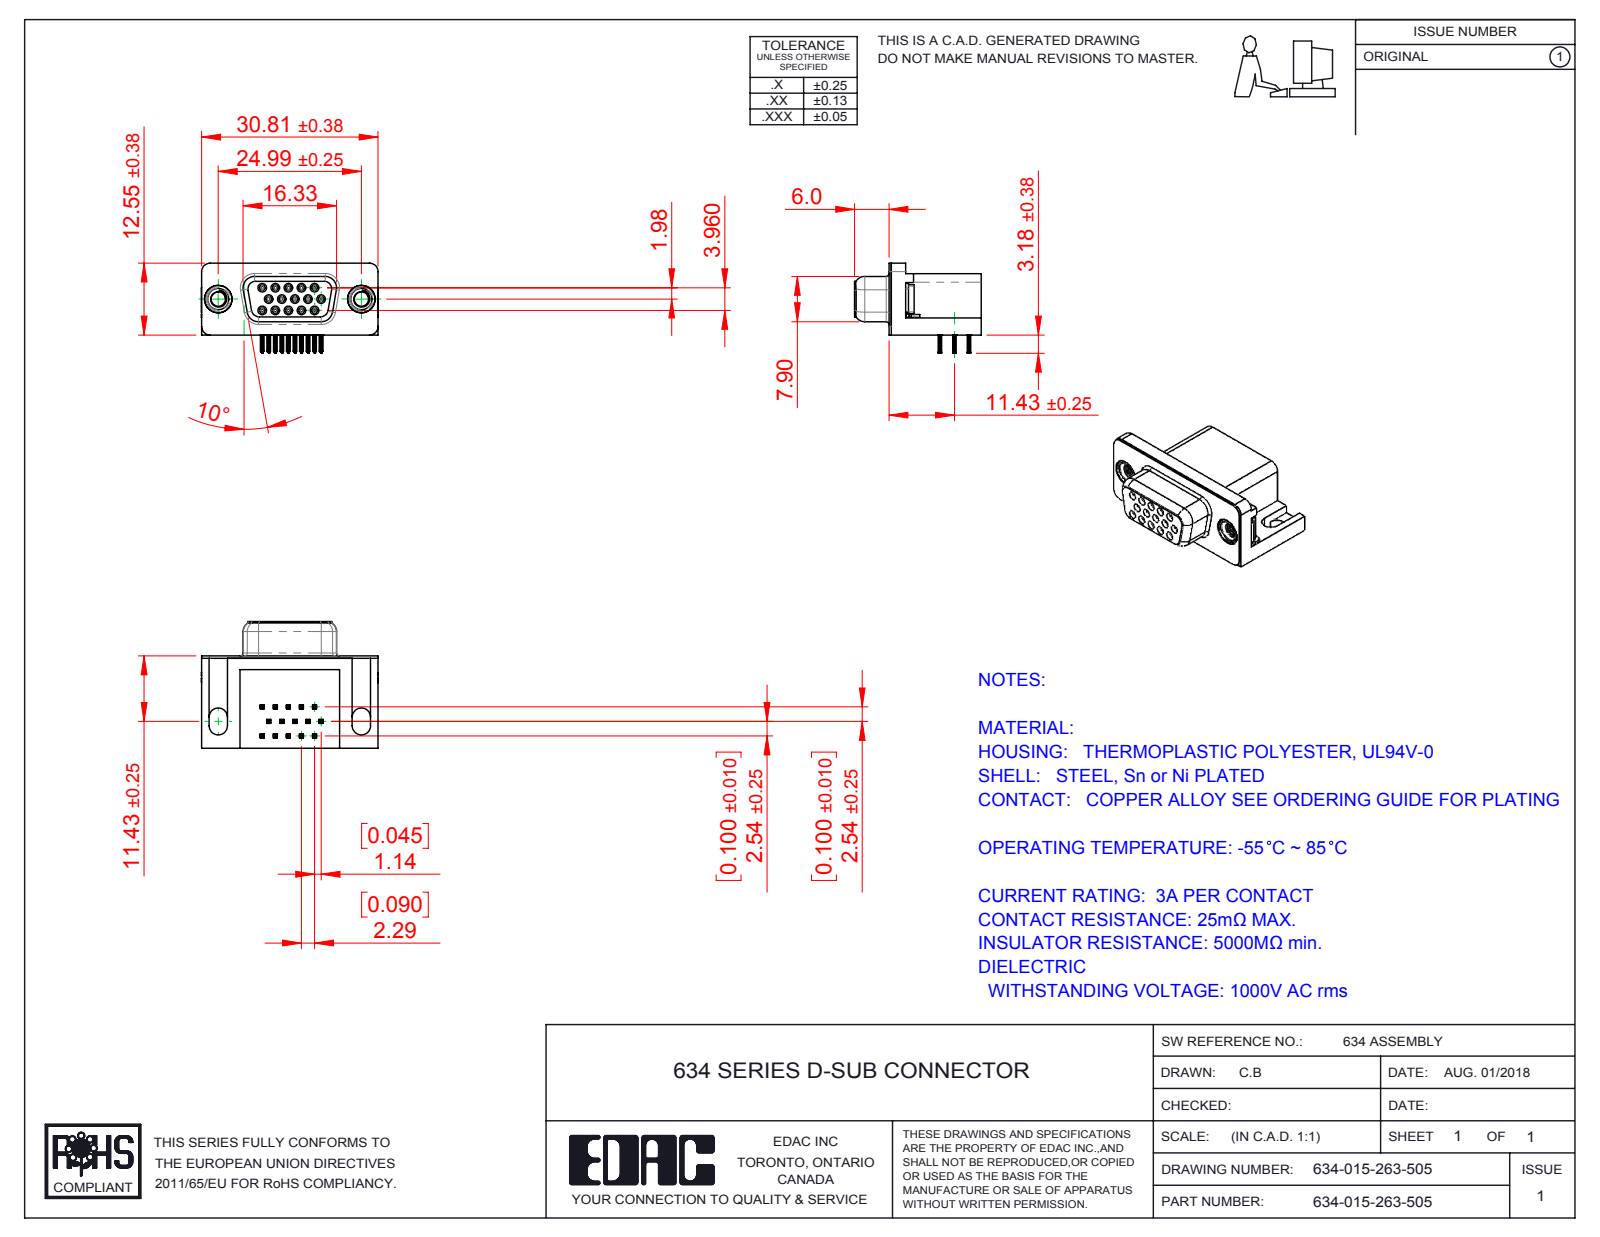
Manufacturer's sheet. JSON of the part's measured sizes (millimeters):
{"part_name": "634 Shell; Non Board Mount; Contact Middle; M3 Threaded Rivet (+4 more)", "step_written_by": "SolidWorks 2016 (CONFIG_CONTROL_DESIGN)", "units": "millimeters", "bodies": {"solids": 21, "faces": 2417, "planar": 1066, "cylindrical": 599, "other": 752}, "overall_size": [30.89, 22.1, 15.73], "volume_mm3": 4500, "surface_area_mm2": 6282, "round_holes": [[0.8, 15], [0.9, 15], [2.5, 2], [4, 2], [4.8, 2], [5, 2]], "round_bosses_or_shafts": [[1.2, 15], [4.9, 2], [4.75, 2], [3.9, 2]], "partial_cylinders_radius": [[0.1, 120], [0.15, 60], [0.35, 30], [1, 19], [0.34, 15], [0.25, 8], [1.35, 8], [1.6, 8]], "face_to_face_distances": [0.4, 10.35, 15.7, 16.1, 2.5, 2.9, 6.4, 0.35, 10.7, 6.7], "hole_center_spacings": [2.29, 2.28, 3.96, 4.57, 6.05, 3.97, 4.58, 6.86]}
